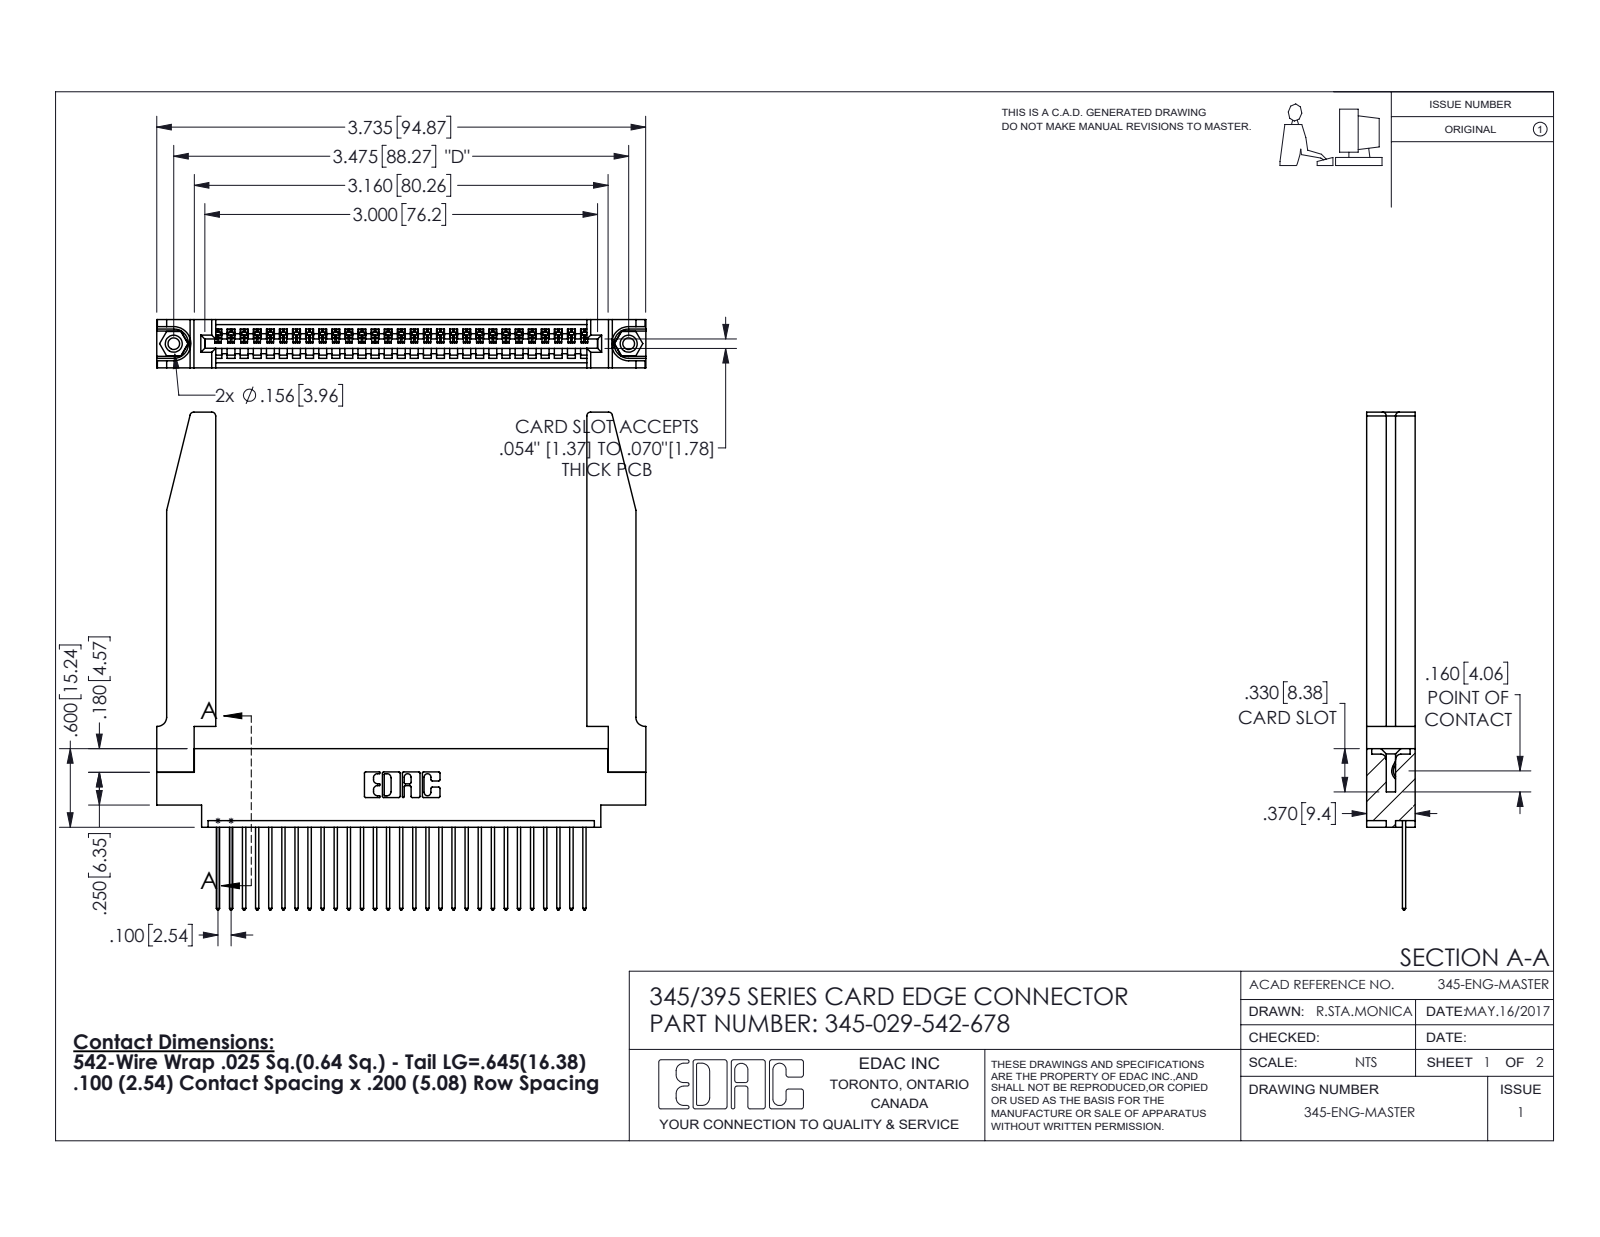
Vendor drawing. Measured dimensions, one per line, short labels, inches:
name: 345-292-001_345-293-142; 345 Part_0.170 Offset - 0.156 Dia-TH; 345-220-078_345-220-078; 345-250-001_345-250-001-102 (+1 more)
written by: SolidWorks 2016 (CONFIG_CONTROL_DESIGN)
unit: in
bodies: 34 solids, 2046 faces (1386 planar, 608 cylindrical, 52 other)
size: 3.802 × 3.736 × 0.37
volume: 1.015 in³; area: 29.41 in²
holes: 2× ⌀0.089, 2× ⌀0.125, 2× ⌀0.156, 1× ⌀0.064
bosses: 2× ⌀0.155
rounds: 58× R0.006, 58× R0.01, 22× R0.01, 8× R0.03, 6× R0.007, 6× R0.031, 3× R0.026, 2× R0.031
face distances: 0.37, 0.072, 0.298, 0.098, 0.272, 0.025, 0.2, 0.148, 0.15, 0.225
hole spacings: 0.27, 3.24, 3.475
